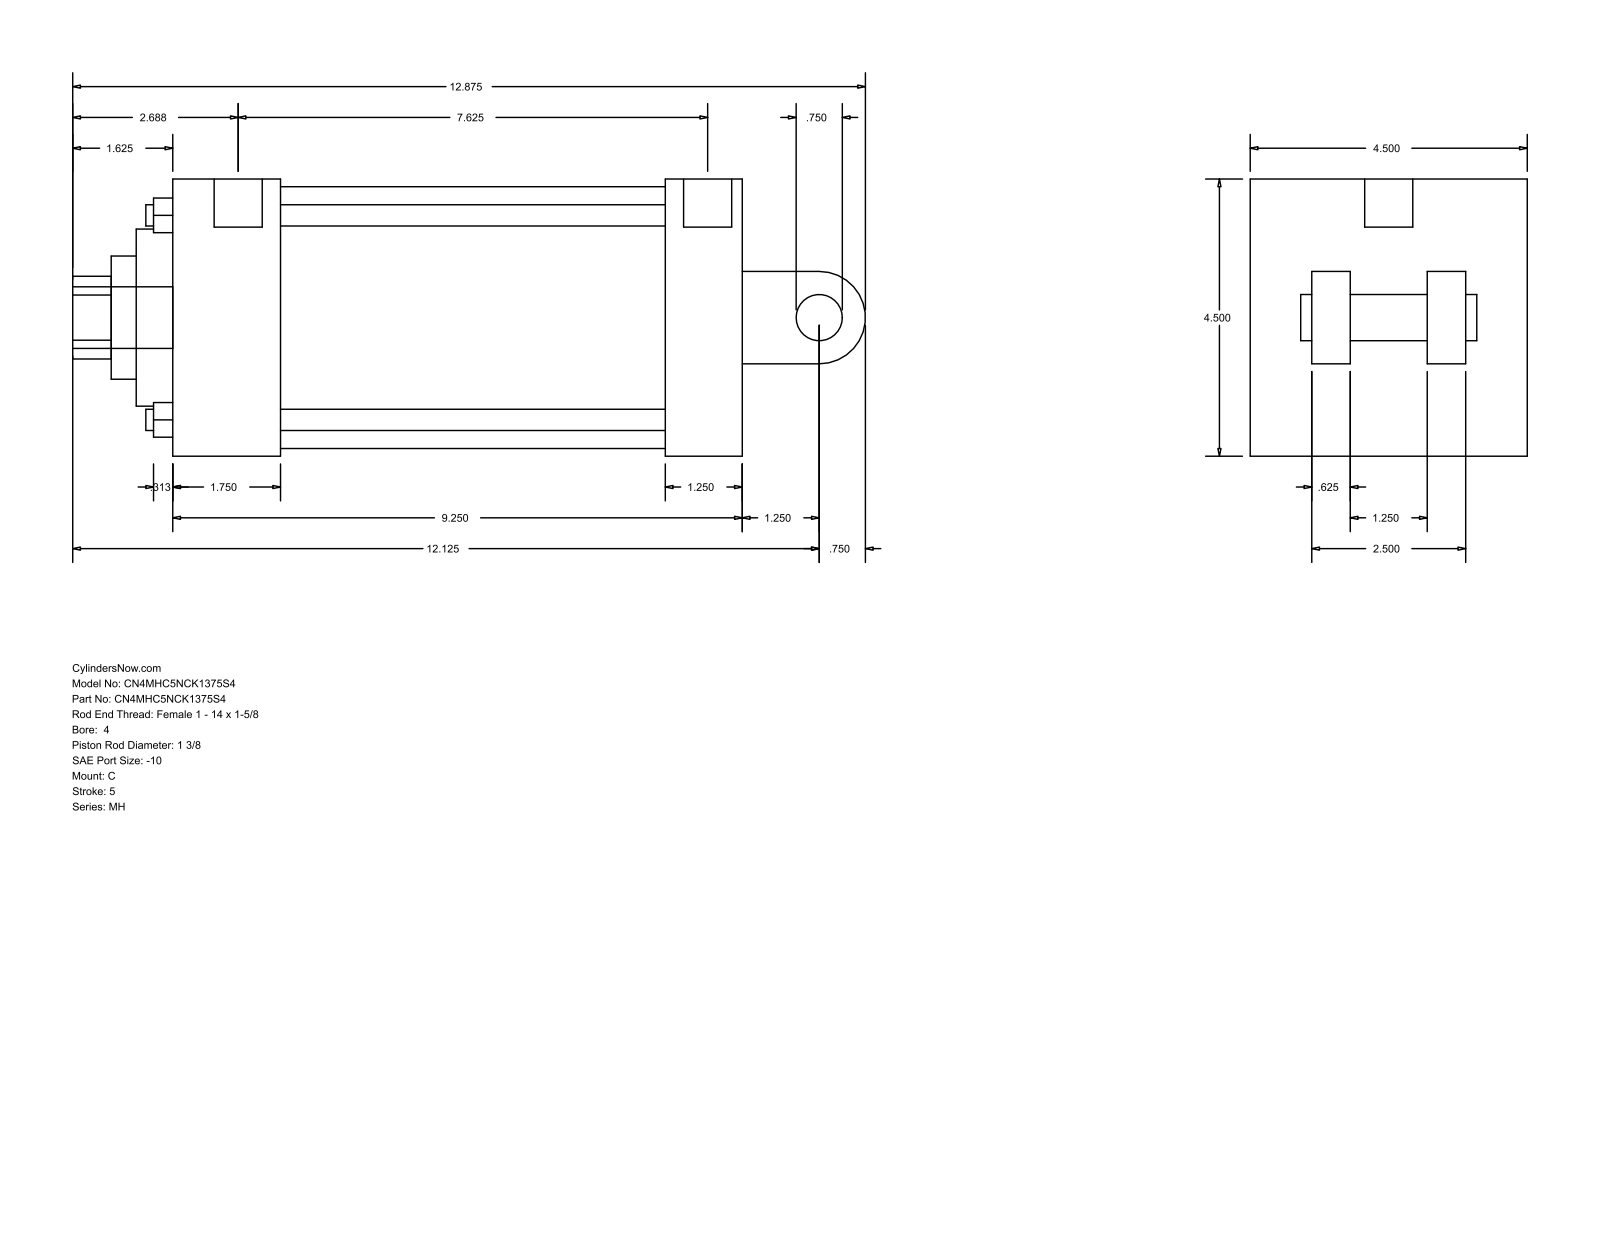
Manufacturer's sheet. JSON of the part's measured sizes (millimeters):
{"part_name": "MH_C__0400_1.375", "step_written_by": "GSSL Pune (CONFIG_CONTROL_DESIGN)", "units": "millimeters", "bodies": {"solids": 0, "faces": 101, "planar": 71, "cylindrical": 30, "other": 0}, "overall_size": [327.02, 114.3, 114.3], "round_holes": [[8.76, 4], [8.73, 2], [19.84, 1], [34.92, 1], [50.8, 1], [73.03, 1], [107.95, 1]], "round_bosses_or_shafts": [[8.73, 2], [25.4, 1], [19.84, 1], [19.05, 1]], "partial_cylinders_radius": [[17.06, 1], [19.05, 1]], "face_to_face_distances": [114.3, 234.96, 31.76, 44.45, 203.2, 158.75, 190.51, 73.03, 41.27, 38.1], "hole_center_spacings": [59.62, 84.32, 119.25, 1.58]}
